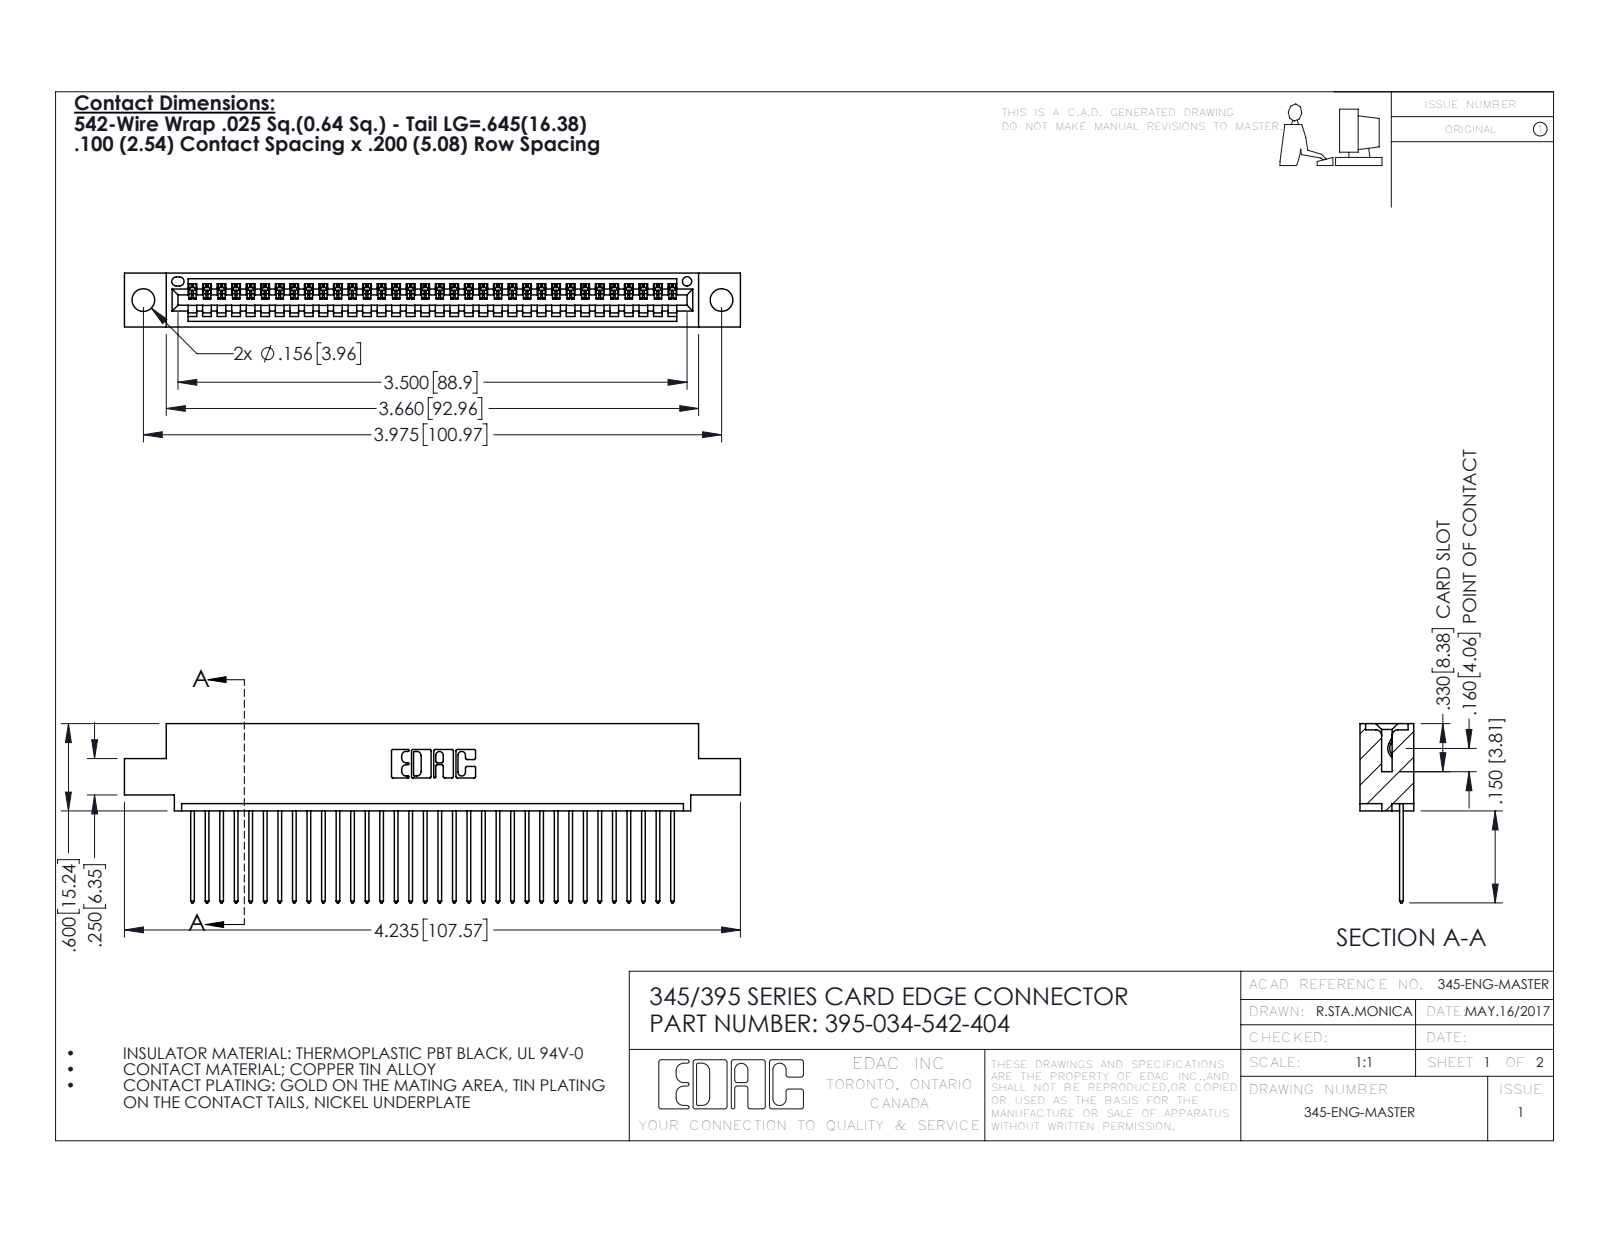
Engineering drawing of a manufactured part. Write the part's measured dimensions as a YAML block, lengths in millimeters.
part_name: "345-292-001_345-293-142; 345 Part_0.110 Offset - 0.156 Dia-TH; 395-034-542-404"
step_written_by: "SolidWorks 2016 (CONFIG_CONTROL_DESIGN)"
units: millimeters
bodies: {solids: 35, faces: 2102, planar: 1444, cylindrical: 658, other: 0}
overall_size: [107.6, 31.3, 9.4]
volume: 10100
surface_area: 13640
round_holes:
  - {diameter: 4, count: 2}
  - {diameter: 1.6, count: 1}
partial_cylinders:
  - {radius: 0.2, count: 68}
  - {radius: 0.3, count: 68}
  - {radius: 0.3, count: 22}
  - {radius: 0.2, count: 6}
  - {radius: 0.8, count: 6}
  - {radius: 0.7, count: 3}
  - {radius: 0.8, count: 2}
  - {radius: 1, count: 2}
face_to_face_distances: [7.6, 1.8, 9.4, 2.5, 6.9, 0.6, 5.1, 5.7, 3.8, 1.8]
hole_center_spacings: [6.9, 95, 101]
